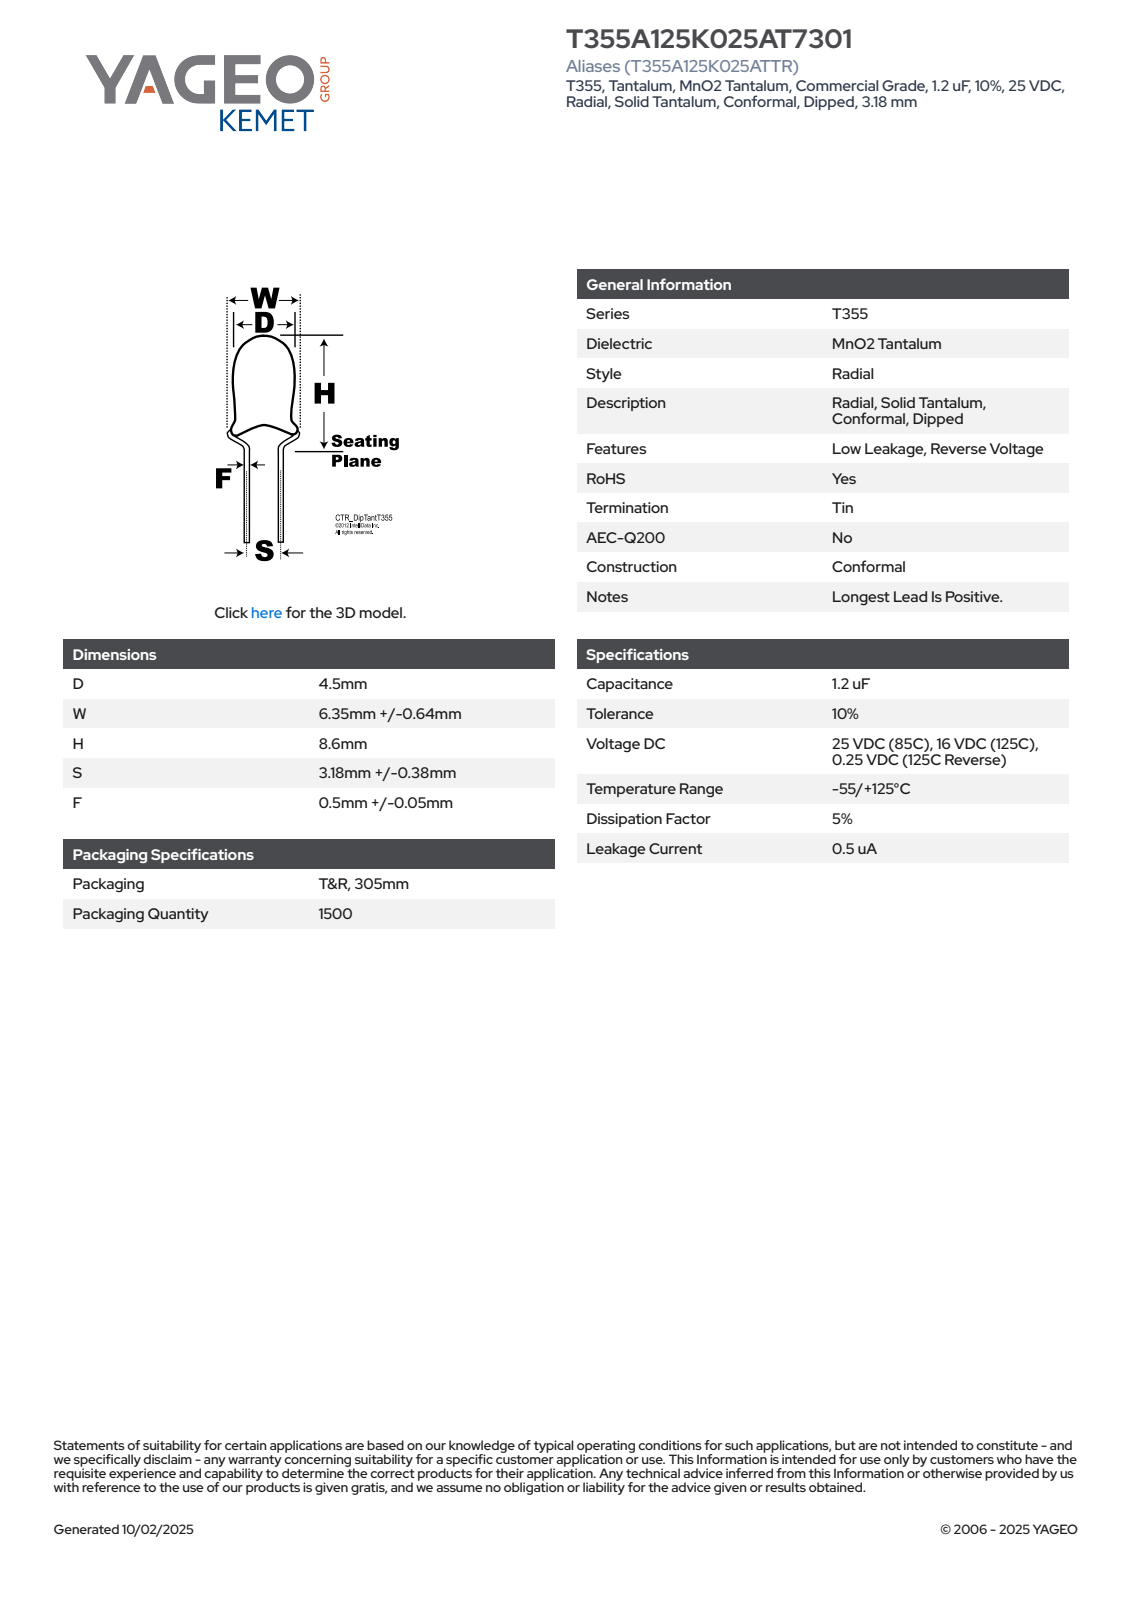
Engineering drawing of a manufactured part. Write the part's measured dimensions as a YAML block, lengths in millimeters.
part_name: "CTR_T355_D4.5W6.99H8.6S3.18LL5.56F0.55"
step_written_by: "SolidWorks 2021 (AUTOMOTIVE_DESIGN)"
units: millimeters
bodies: {solids: 1, faces: 100, planar: 30, cylindrical: 6, other: 64}
overall_size: [14.16, 6.99, 4.5]
volume: 87
surface_area: 135
round_bosses_or_shafts:
  - {diameter: 4.5, count: 1}
partial_cylinders:
  - {radius: 2.24, count: 1}
face_to_face_distances: [6, 8.16, 14.16, 11.53, 3.37, 2.63, 10.92, 2.76, 0.61, 3.24]
